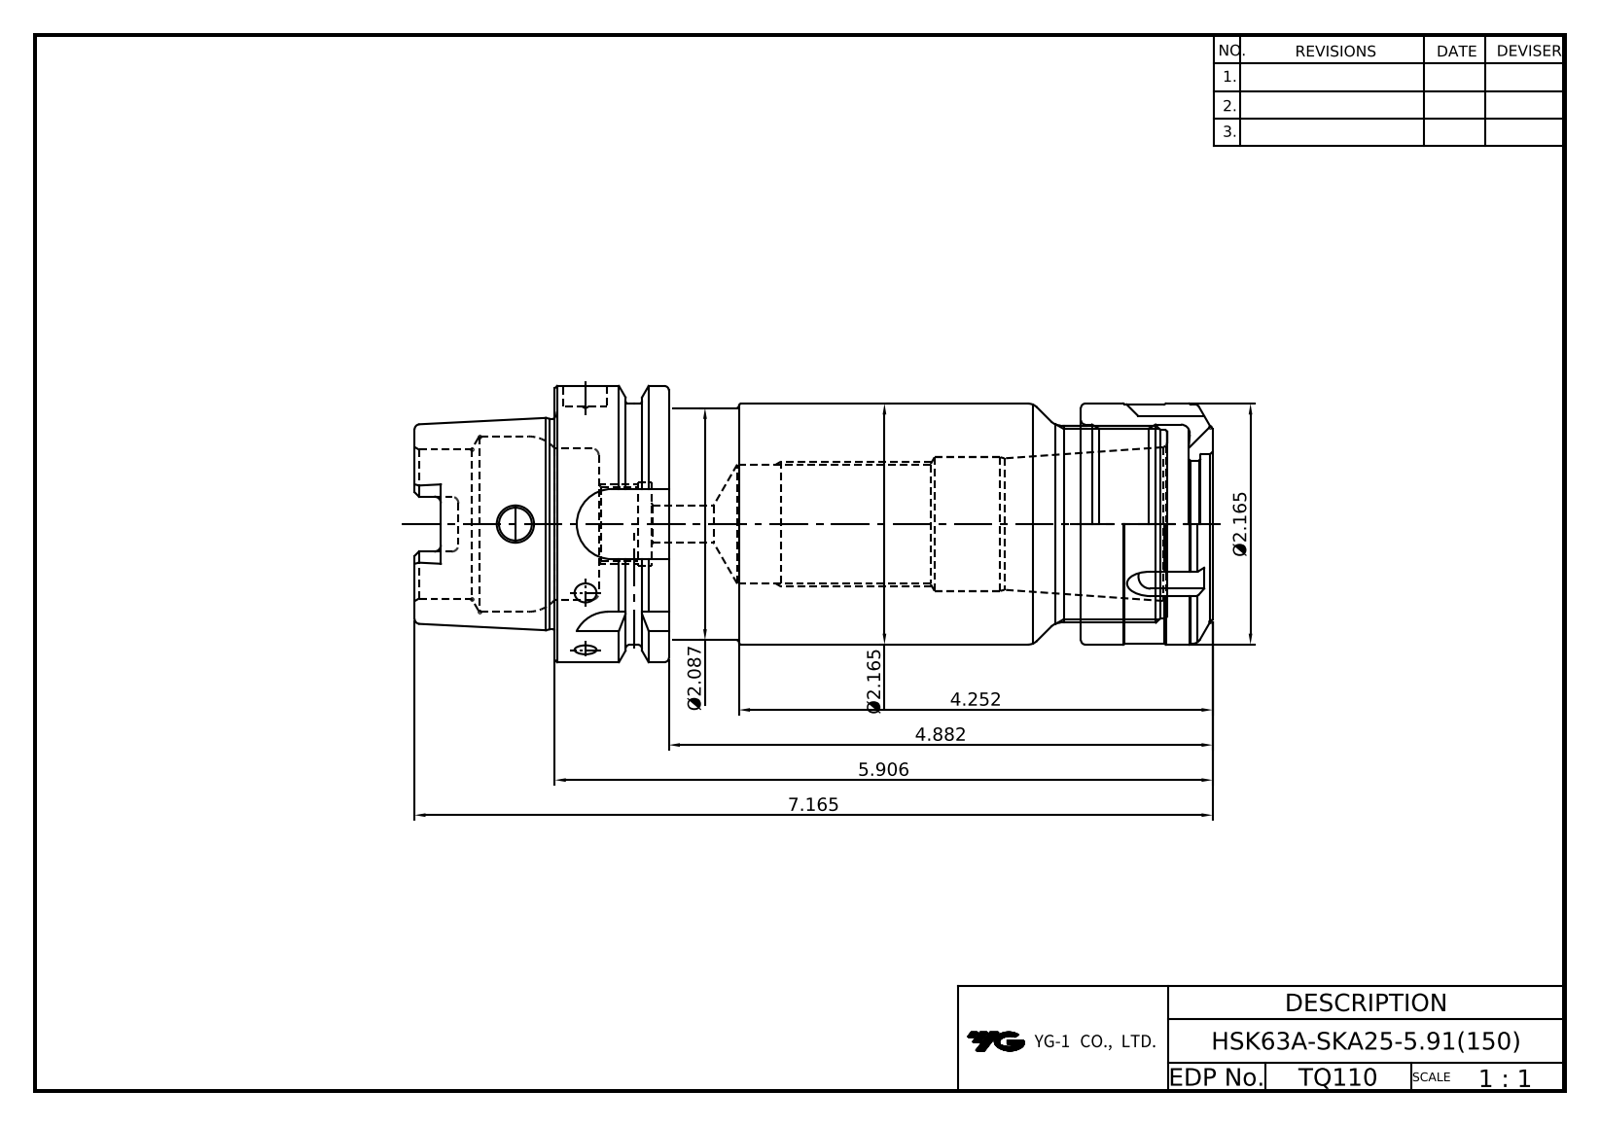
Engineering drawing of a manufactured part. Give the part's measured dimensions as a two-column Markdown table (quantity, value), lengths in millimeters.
| quantity | value |
| --- | --- |
| part name | LO-HSK63A-SKA25-150; SKN25-NUT |
| STEP written by | Autodesk Inventor 2024 (AUTOMOTIVE_DESIGN) |
| units | millimeters |
| bodies | 2 solids, 205 faces (67 planar, 50 cylindrical, 88 other) |
| overall size | 182 × 63 × 63 |
| volume | 283 328 mm³ |
| surface area | 61 711 mm² |
| round holes (diameter × count) | 7.5 × 1, 8 × 1, 10 × 1, 16.92 × 1, 19 × 1, 26.85 × 1, 30.5 × 1, 34 × 1, 34.2 × 1, 36 × 1, 40 × 1, 43.38 × 1 |
| round bosses / shafts (diameter × count) | 63 × 1, 55 × 1, 54.6 × 1, 53 × 1, 48.04 × 1, 45 × 1, 43 × 1 |
| partial cylindrical surfaces (radius × count) | 1.5 × 6, 2.88 × 4, 8 × 4 |
| main face-to-face distances | 150, 10, 26, 124, 120, 140, 16, 110, 94, 30 |
